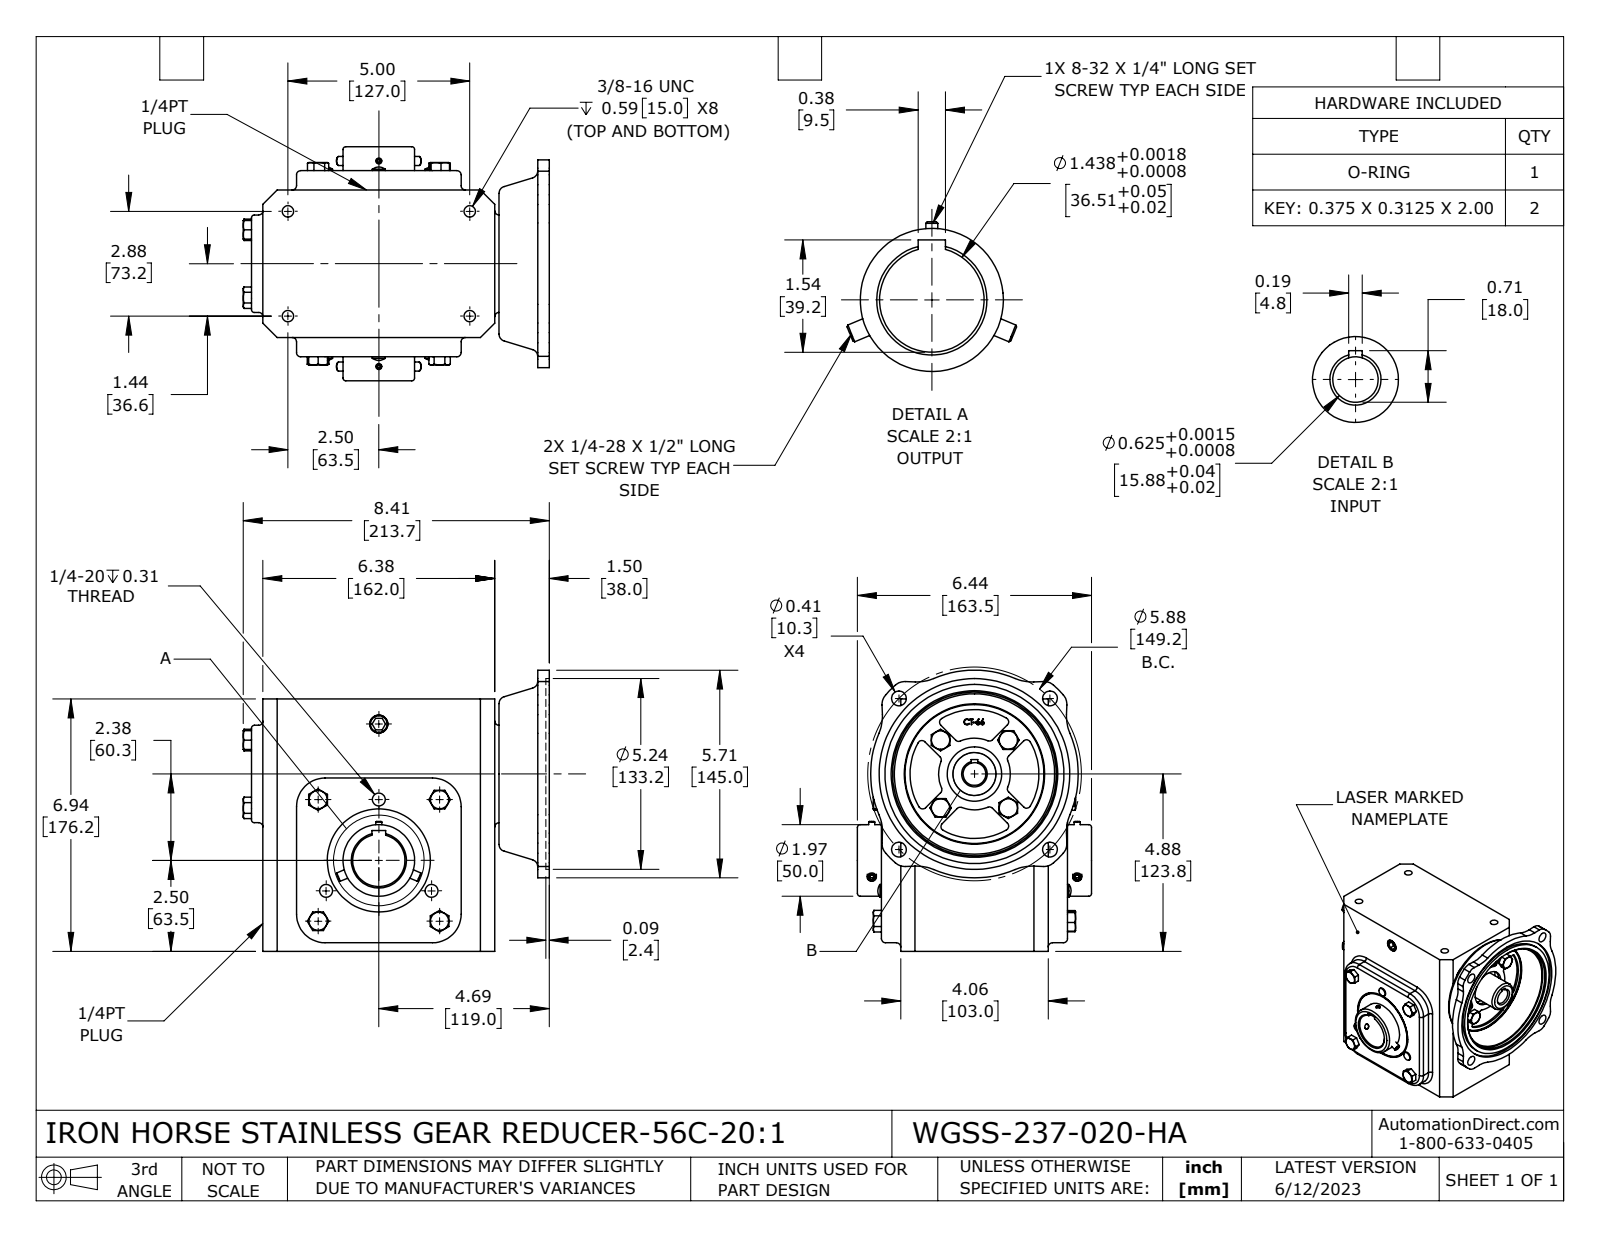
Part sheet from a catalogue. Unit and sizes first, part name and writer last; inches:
Units: inches
Overall size (bounding box): 8.412 × 7.729 × 6.437
Round holes (diameter × count): ⌀0.213 ×4, ⌀0.313 ×4, ⌀0.406 ×4, ⌀0.136 ×2, ⌀0.625 ×1, ⌀0.866 ×1, ⌀1.437 ×1, ⌀1.441 ×1, ⌀1.496 ×1, ⌀1.772 ×1, ⌀3.819 ×1, ⌀4.5 ×1
Round bosses / shafts (diameter × count): ⌀0.25 ×4, ⌀0.354 ×3, ⌀0.164 ×2, ⌀4.921 ×1, ⌀2.835 ×1, ⌀1.969 ×1, ⌀1.181 ×1
Partial cylindrical surfaces — rounded edges, fillets, slot ends (radius × count): R0.118 ×40, R0.394 ×12, R1.181 ×8, R0.079 ×4, R0.787 ×4, R0.984 ×1, R1.772 ×1, R2.854 ×1
Main face-to-face distances: 0.531, 4.587, 6.937, 0.315, 4.055, 6.378, 5.118, 7.874, 1.181, 6.693
Hole centre spacings: 2.858, 2.937, 4.944, 5.65, 2.88, 4.154, 4.154, 5
Volume: 204.5 in³ · Surface area: 348.1 in²
Bodies: 7 solids, 670 faces (287 planar, 195 cylindrical, 188 other)
Part name (STEP PRODUCT): WGSS-237-020-HA
STEP written by: SolidWorks 2021 (CONFIG_CONTROL_DESIGN)
